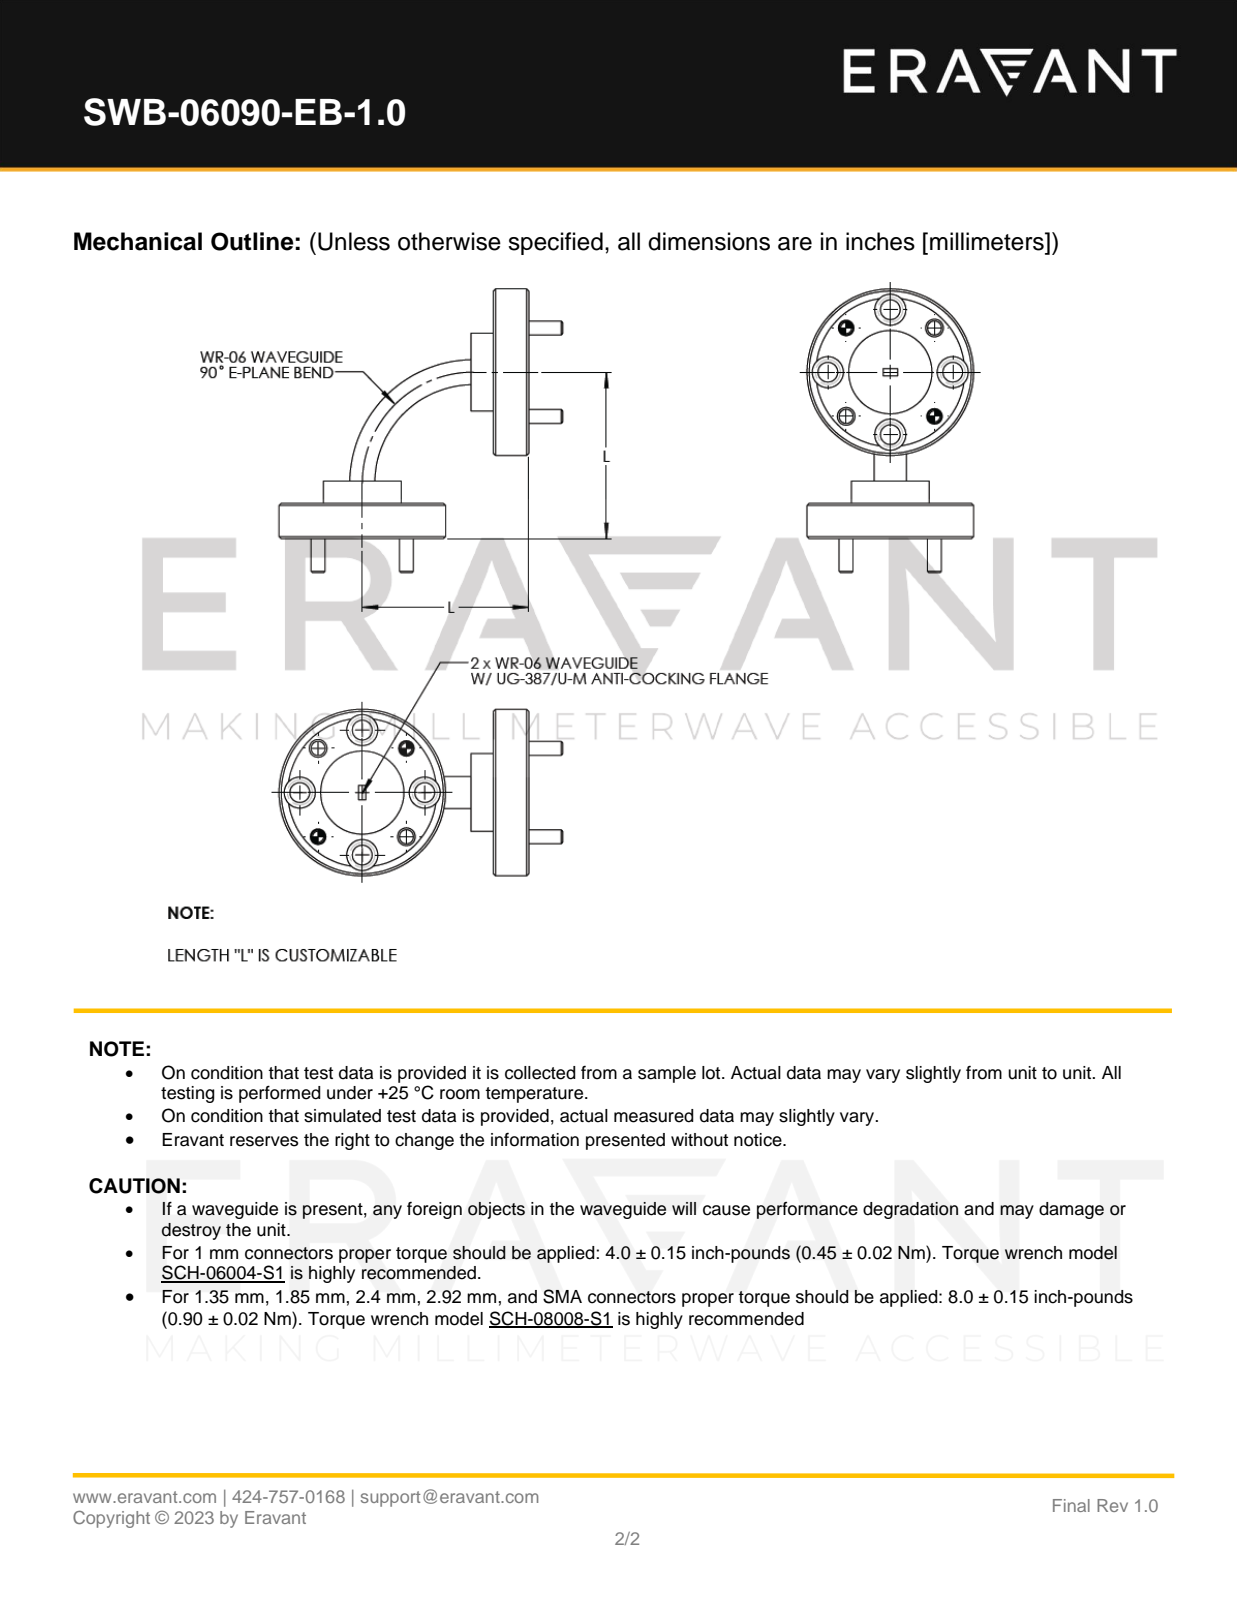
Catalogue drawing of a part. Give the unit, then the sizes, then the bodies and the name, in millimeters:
Units: millimetres
Overall size (bounding box): 38.8 × 38.8 × 19.1
Round holes (diameter × count): ⌀2.3 ×8, ⌀3.6 ×8, ⌀1.5 ×4, ⌀1.7 ×4, ⌀17.3 ×2
Round bosses / shafts (diameter × count): ⌀1.6 ×4, ⌀19.1 ×2, ⌀9.5 ×2, ⌀8.9 ×2
Partial cylindrical surfaces — rounded edges, fillets, slot ends (radius × count): R8.4 ×1, R12 ×1
Main face-to-face distances: 4.1, 0.5, 3.6, 2.5, 5.1, 23.6, 27.2, 23.1, 26.7, 19.6
Hole centre spacings: 5.5, 10.1, 7.1, 13.2, 13.2, 14.3, 7.1, 14.3
Volume: 2 920 mm³ · Surface area: 2 832 mm²
Bodies: 5 solids, 156 faces (42 planar, 78 cylindrical, 36 other)
Part name (STEP PRODUCT): WB-ED-A-L, Defeatured
STEP written by: SolidWorks 2021 (AUTOMOTIVE_DESIGN)
